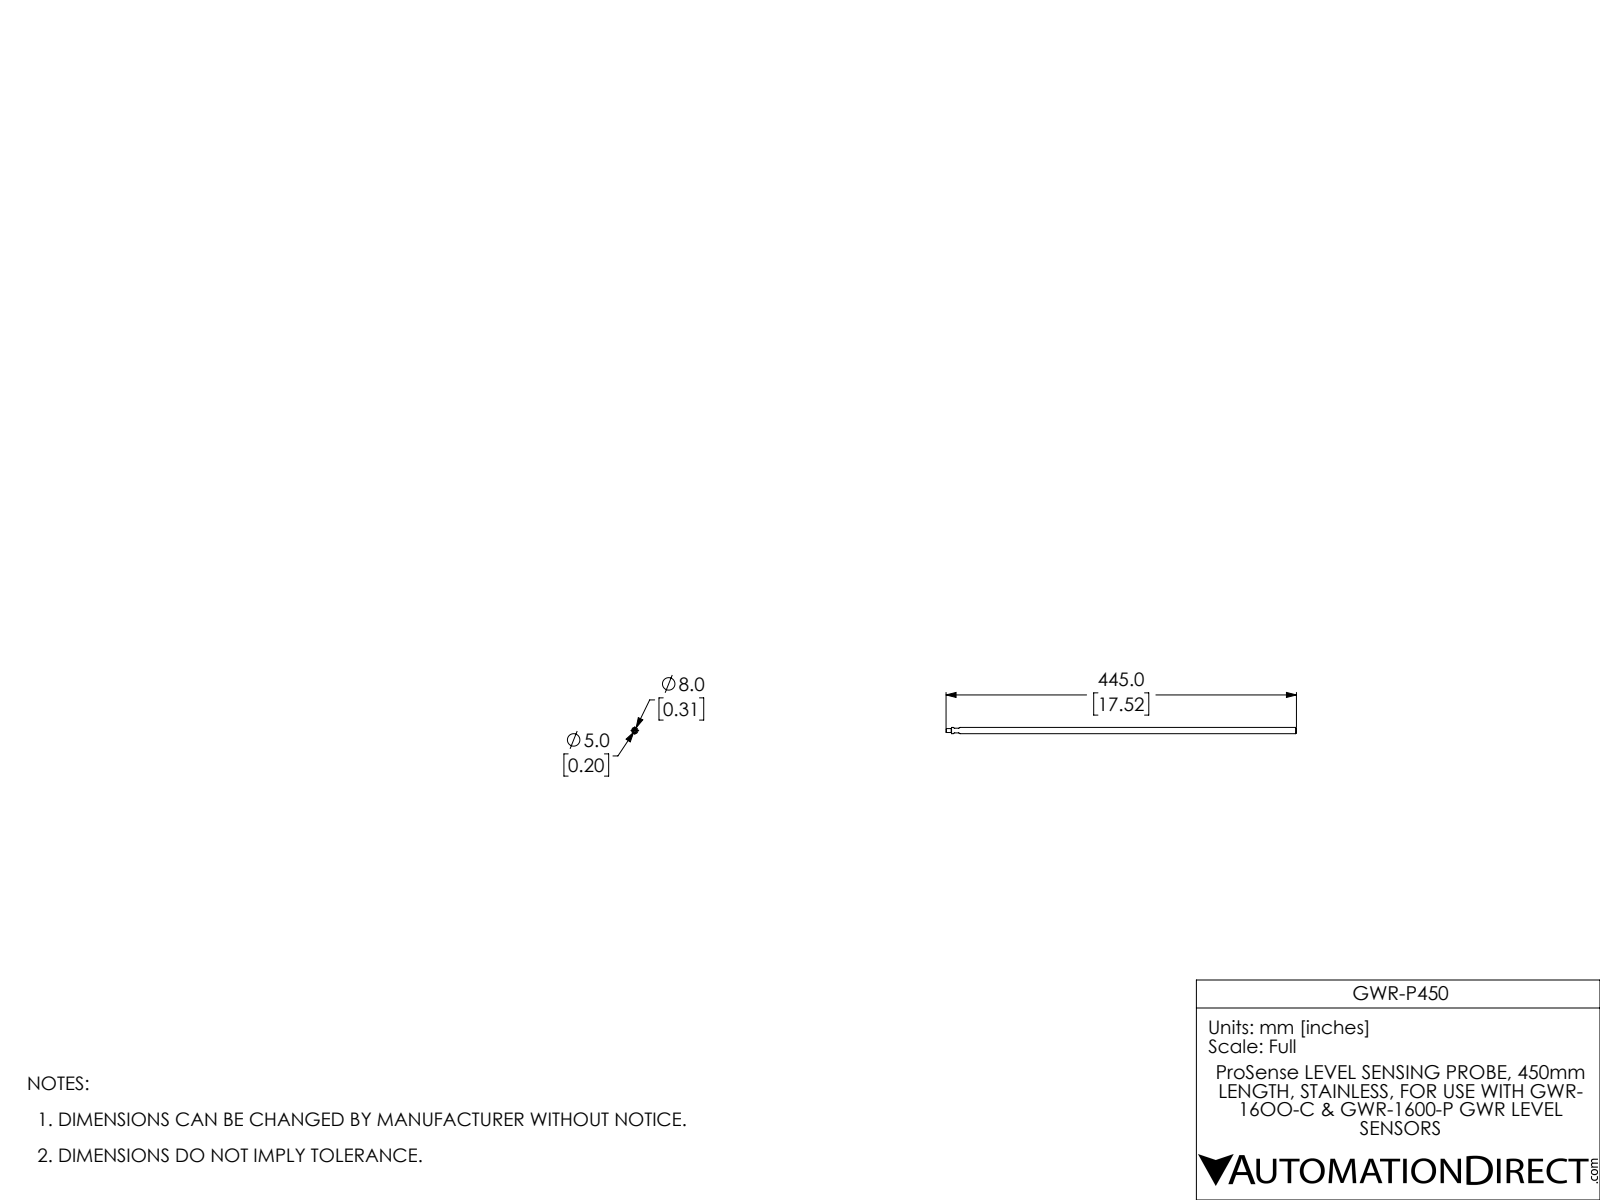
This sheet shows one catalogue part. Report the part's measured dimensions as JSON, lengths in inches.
{"part_name": "GWR-P450", "step_written_by": "SolidWorks 2017 (AUTOMOTIVE_DESIGN)", "units": "inches", "bodies": {"solids": 1, "faces": 19, "planar": 5, "cylindrical": 8, "other": 6}, "overall_size": [17.52, 0.315, 0.315], "volume_in3": 1.348, "surface_area_in2": 17.37, "round_bosses_or_shafts": [[0.315, 1], [0.197, 1]], "partial_cylinders_radius": [[0.079, 4]], "face_to_face_distances": [17.244, 0.236, 17.52, 0.276]}
